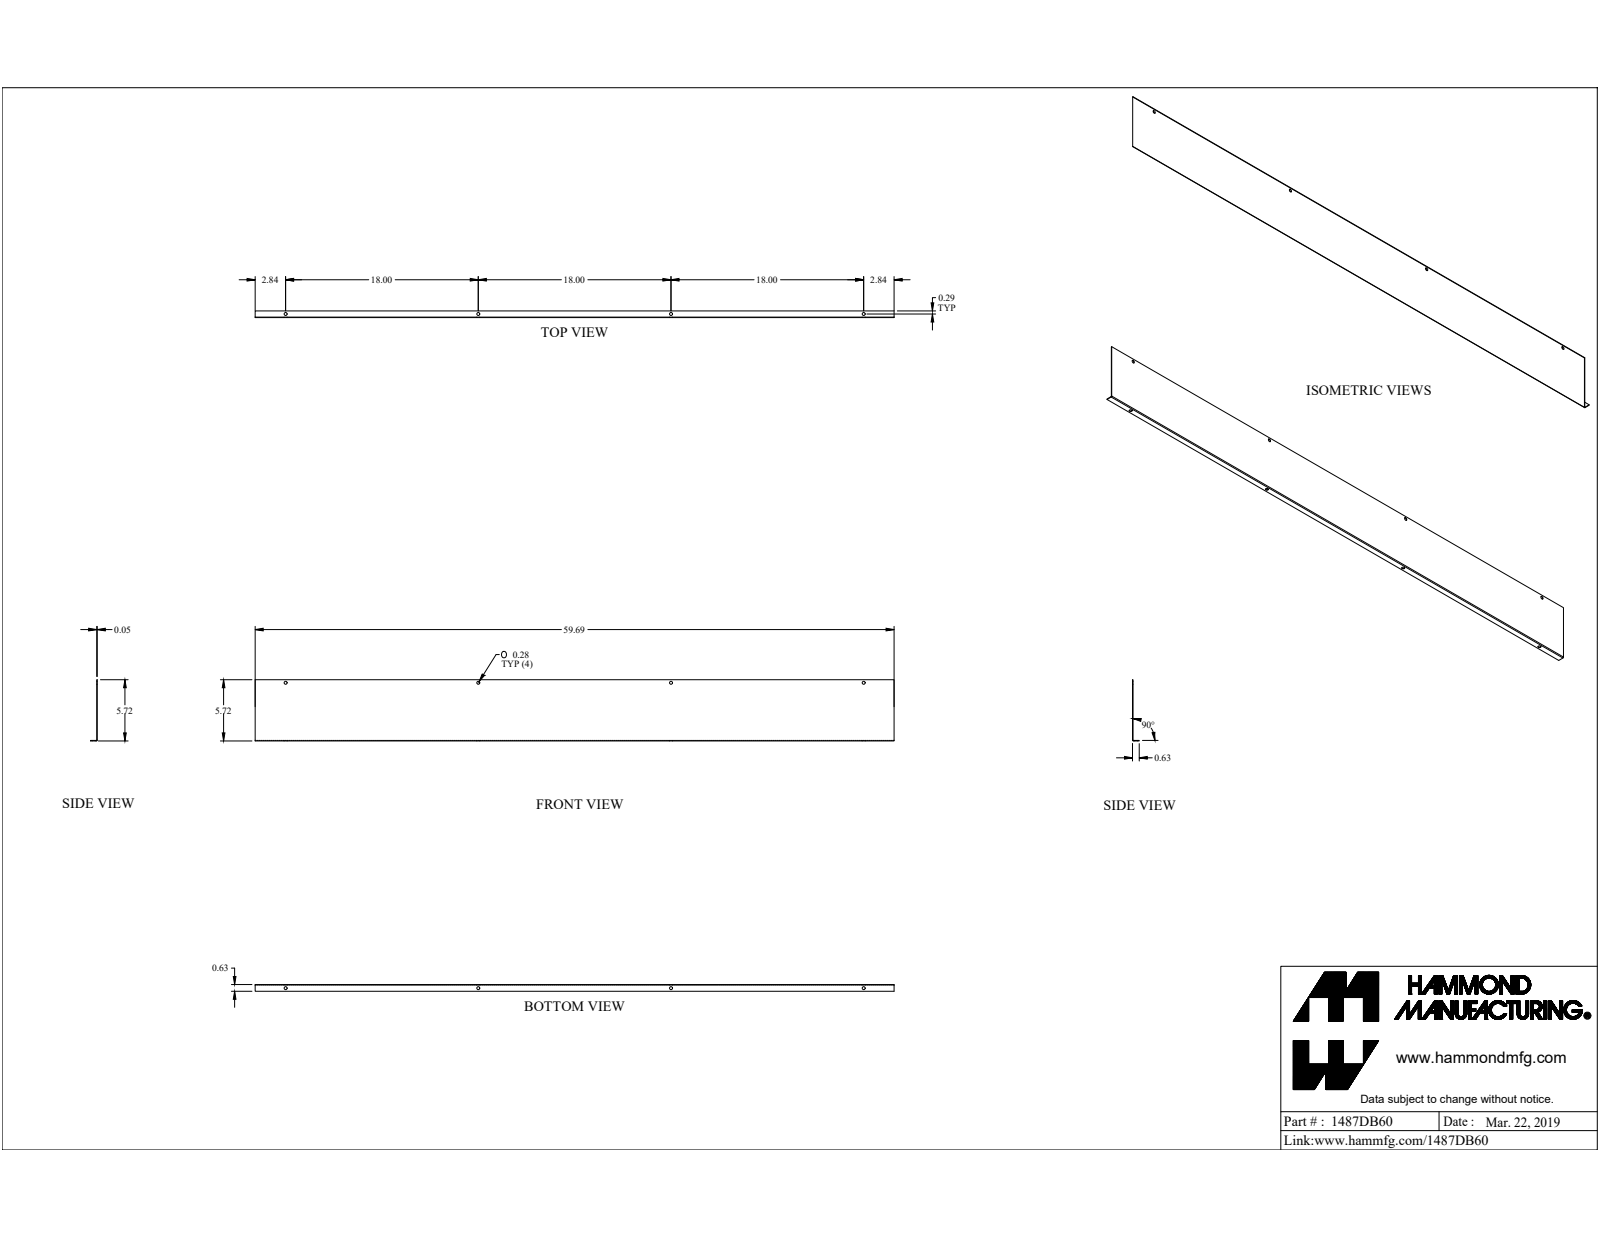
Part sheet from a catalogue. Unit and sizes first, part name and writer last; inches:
Units: inches
Overall size (bounding box): 59.687 × 6.218 × 0.844
Round holes (diameter × count): ⌀0.281 ×8, ⌀0.25 ×1, ⌀0.26 ×1
Round bosses / shafts (diameter × count): ⌀0.51 ×1, ⌀0.438 ×1, ⌀0.224 ×1
Partial cylindrical surfaces — rounded edges, fillets, slot ends (radius × count): R0.024 ×1, R0.072 ×1
Main face-to-face distances: 0.048, 0.625, 0.577, 5.718, 5.67, 59.687, 0.03, 0.018, 0.595, 0.438
Hole centre spacings: 18, 36, 9.006, 27.002, 54, 10.511, 10.511, 27.54
Volume: 18.02 in³ · Surface area: 756.6 in²
Bodies: 4 solids, 63 faces (33 planar, 15 cylindrical, 15 other)
Part name (STEP PRODUCT): 1487DB60
STEP written by: SolidWorks 2019 (CONFIG_CONTROL_DESIGN)
